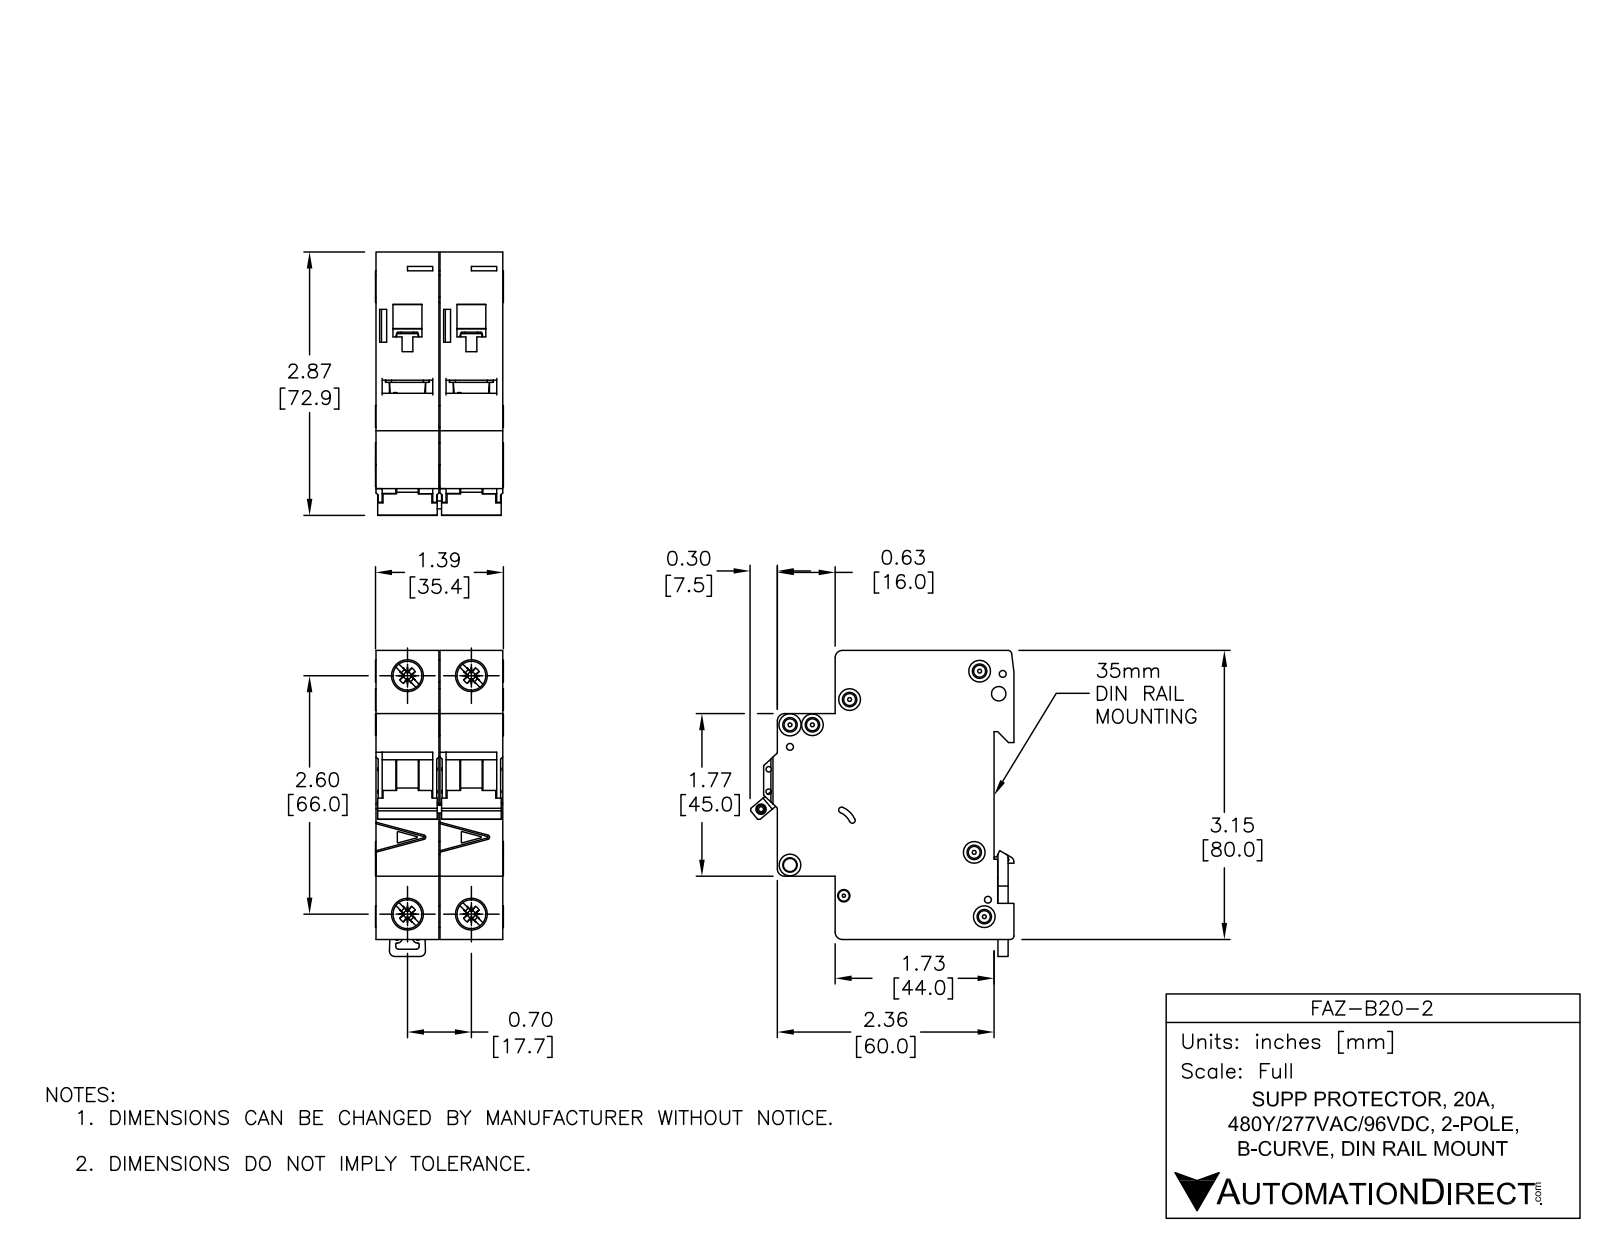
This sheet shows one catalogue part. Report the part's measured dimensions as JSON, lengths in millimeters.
{"part_name": "FAZ-B20-2", "step_written_by": "SolidWorks 2014 (AUTOMOTIVE_DESIGN)", "units": "millimeters", "bodies": {"solids": 8, "faces": 1104, "planar": 466, "cylindrical": 396, "other": 242}, "overall_size": [84.78, 73.04, 35.4], "volume_mm3": 149808, "surface_area_mm2": 38799, "round_holes": [[3.6, 6], [1.9, 3], [1.09, 2], [1.5, 2], [4, 2], [7.15, 2], [8.2, 2], [2.15, 1], [2.2, 1], [2.55, 1], [3.3, 1], [3.4, 1]], "round_bosses_or_shafts": [[6, 4], [8.2, 2], [2.5, 2]], "partial_cylinders_radius": [[0.25, 49], [0.5, 19], [2, 10], [0.2, 8], [1, 8], [0.8, 2], [1.8, 2], [3, 2]], "face_to_face_distances": [17.7, 17.5, 35.2, 79.48, 5.5, 49.5, 44, 65.5, 60, 16], "hole_center_spacings": [6.2, 13.64, 17.7, 66, 68.33, 4.81, 5.19, 5.61]}
